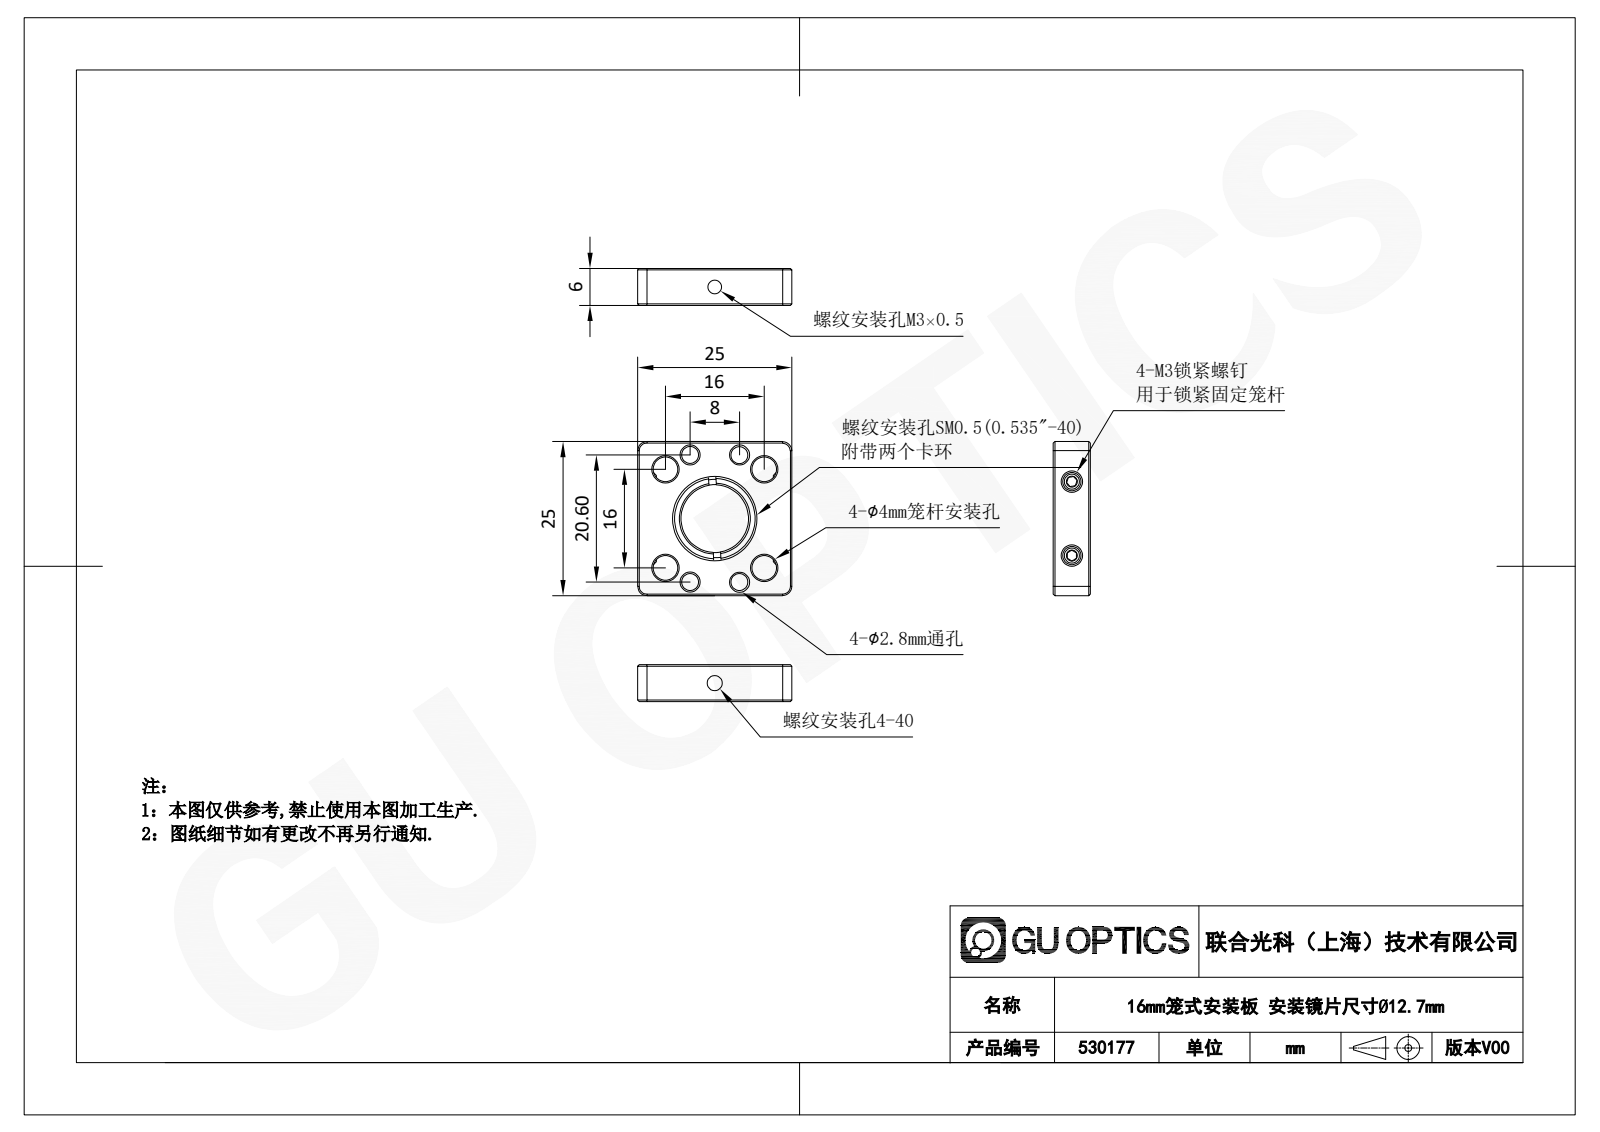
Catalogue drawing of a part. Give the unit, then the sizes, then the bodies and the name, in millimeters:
Units: millimetres
Overall size (bounding box): 25 × 25 × 6
Round holes (diameter × count): ⌀2.8 ×4, ⌀4 ×4, ⌀2.5 ×3, ⌀2.26 ×1, ⌀11 ×1, ⌀12.69 ×1
Round bosses / shafts (diameter × count): ⌀3 ×2, ⌀13.59 ×1
Partial cylindrical surfaces — rounded edges, fillets, slot ends (radius × count): R1.5 ×4
Main face-to-face distances: 6, 25, 2, 4, 21.56, 3, 22, 1.5, 1, 24
Hole centre spacings: 4.61, 11.05, 11.31, 12.22, 16, 18.73, 21.88, 8
Volume: 2 630 mm³ · Surface area: 2 901 mm²
Bodies: 7 solids, 321 faces (153 planar, 27 cylindrical, 141 other)
Part name (STEP PRODUCT): 530177
STEP written by: SolidWorks 2020 (CONFIG_CONTROL_DESIGN)
